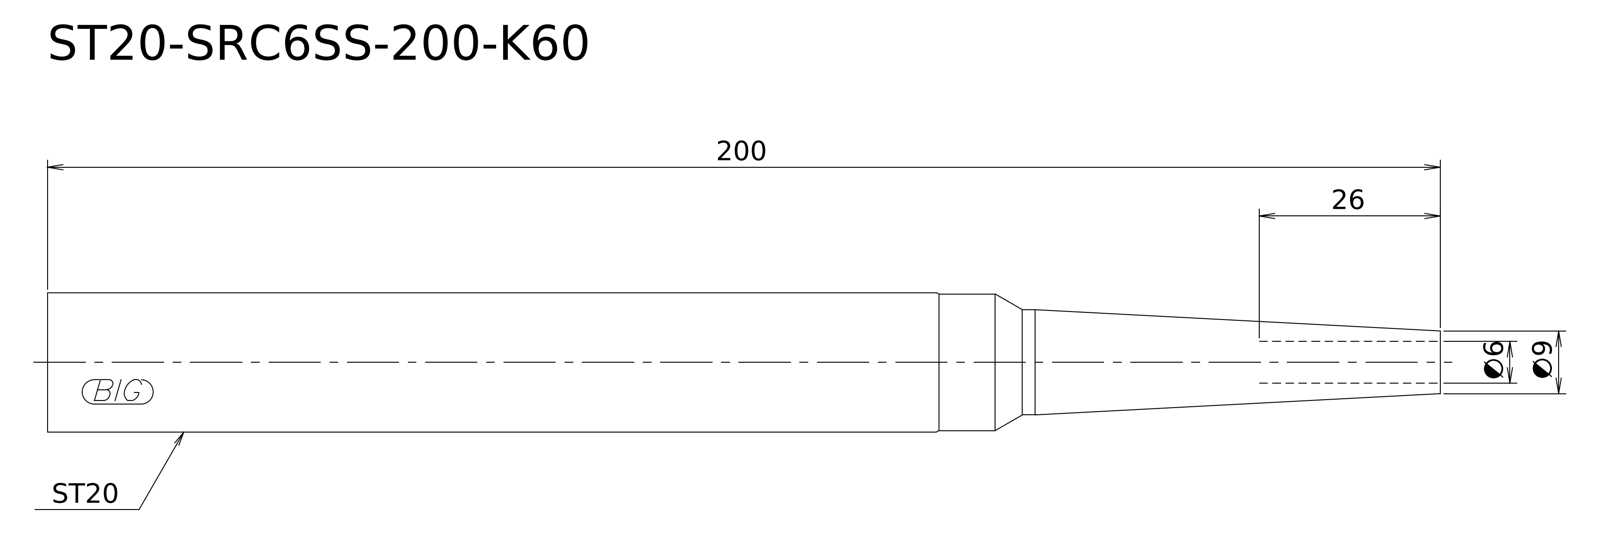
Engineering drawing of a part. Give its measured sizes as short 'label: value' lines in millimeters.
written by: Kubotek KeyCreator V8.5.1 (14335) (CONFIG_CONTROL_DESIGN)
unit: mm
bodies: 1 solid, 8 faces (2 planar, 3 cylindrical, 3 other)
size: 200 × 20 × 20
volume: 50 683 mm³; area: 11 459 mm²
bosses: 1× ⌀20, 1× ⌀19.6, 1× ⌀15.1
face distances: 200
